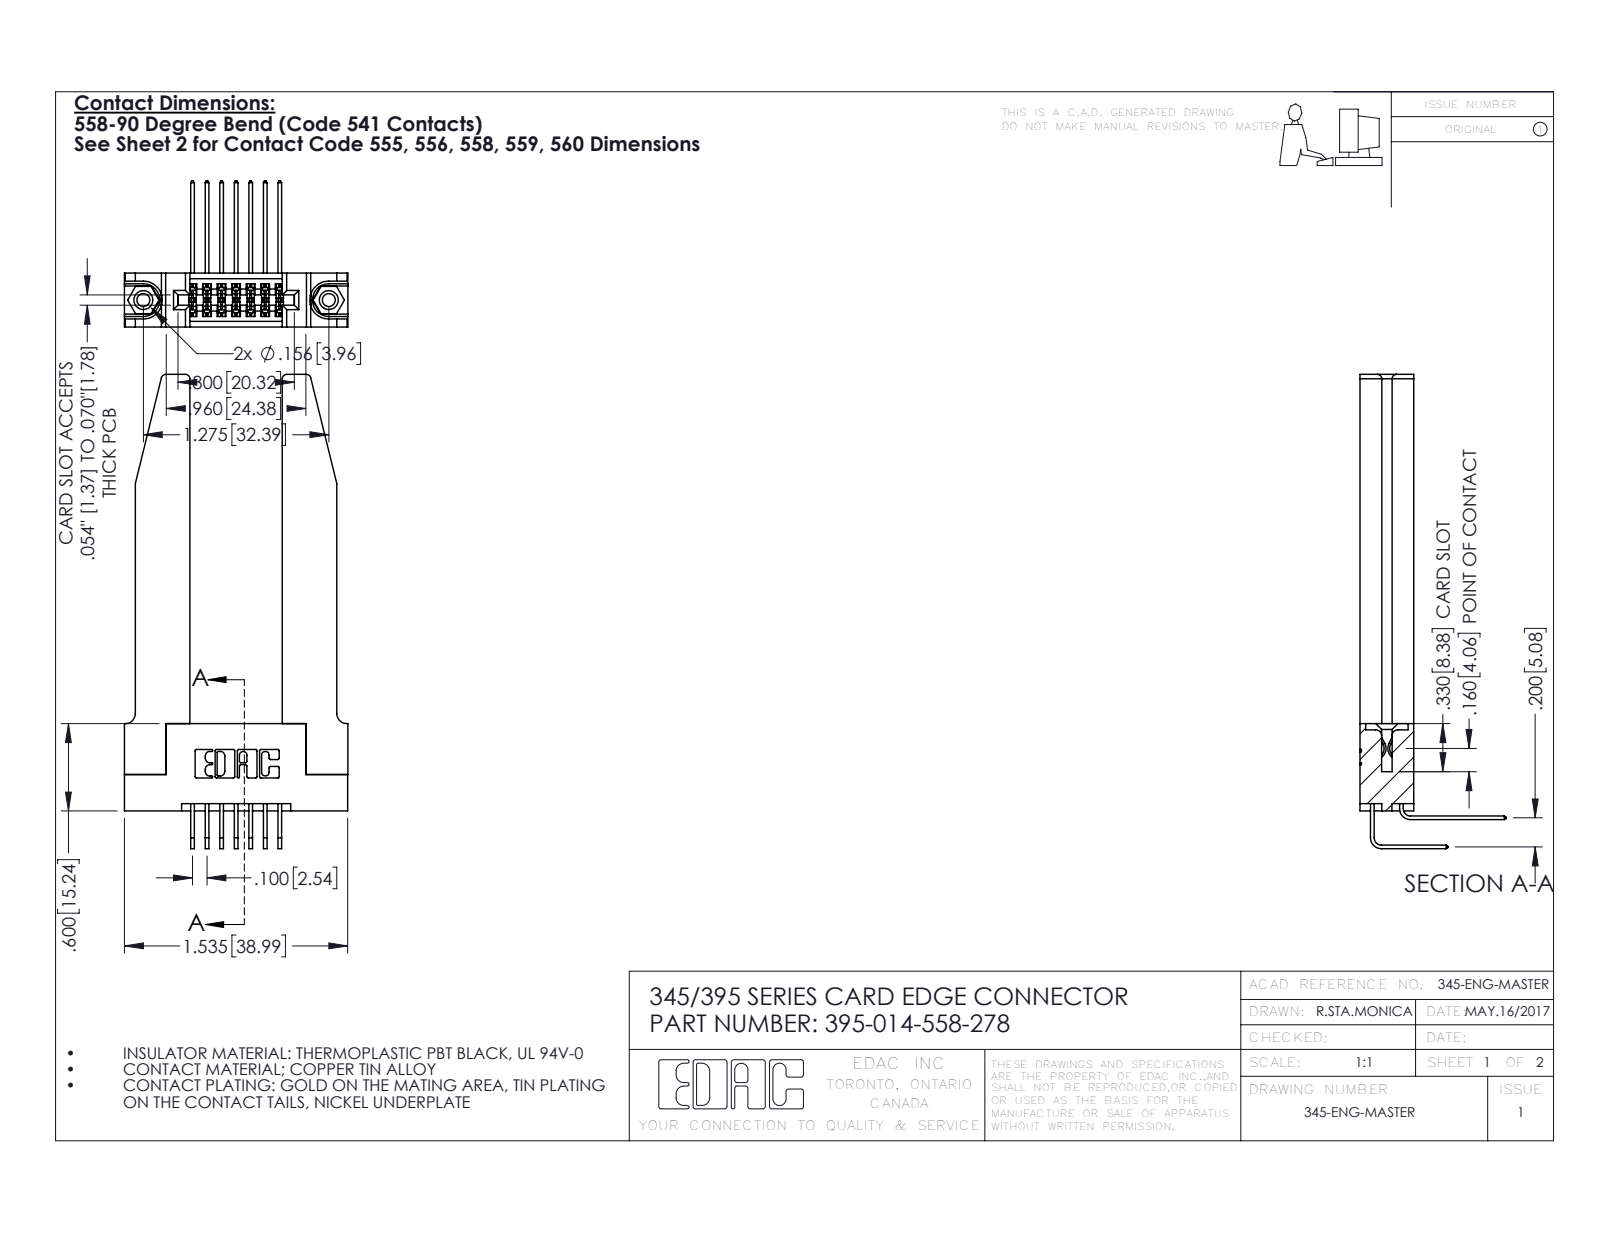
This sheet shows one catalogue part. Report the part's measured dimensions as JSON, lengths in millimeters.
{"part_name": "345-292-001_558 Tail - 2; 395-014-558-278; 345-292-001_558 559 Tail - 1; 345 Part_Flush Mounting Lugs - 0.156 Dia-TH (+2 more)", "step_written_by": "SolidWorks 2016 (CONFIG_CONTROL_DESIGN)", "units": "millimeters", "bodies": {"solids": 19, "faces": 1088, "planar": 712, "cylindrical": 324, "other": 52}, "overall_size": [82.8, 39, 25.5], "volume_mm3": 11300, "surface_area_mm2": 11780, "round_holes": [[2.3, 2], [3.2, 2], [4, 2], [1.6, 1]], "round_bosses_or_shafts": [[3.9, 2]], "partial_cylinders_radius": [[0.2, 22], [0.3, 22], [0.8, 8], [0.2, 6], [0.8, 6], [0.7, 3], [0.4, 2], [0.5, 2]], "face_to_face_distances": [9.4, 3.8, 1.8, 3.8, 5.1, 5.6, 7.6, 2, 16.1, 2.4], "hole_center_spacings": [6.9, 26.5, 32.4]}
